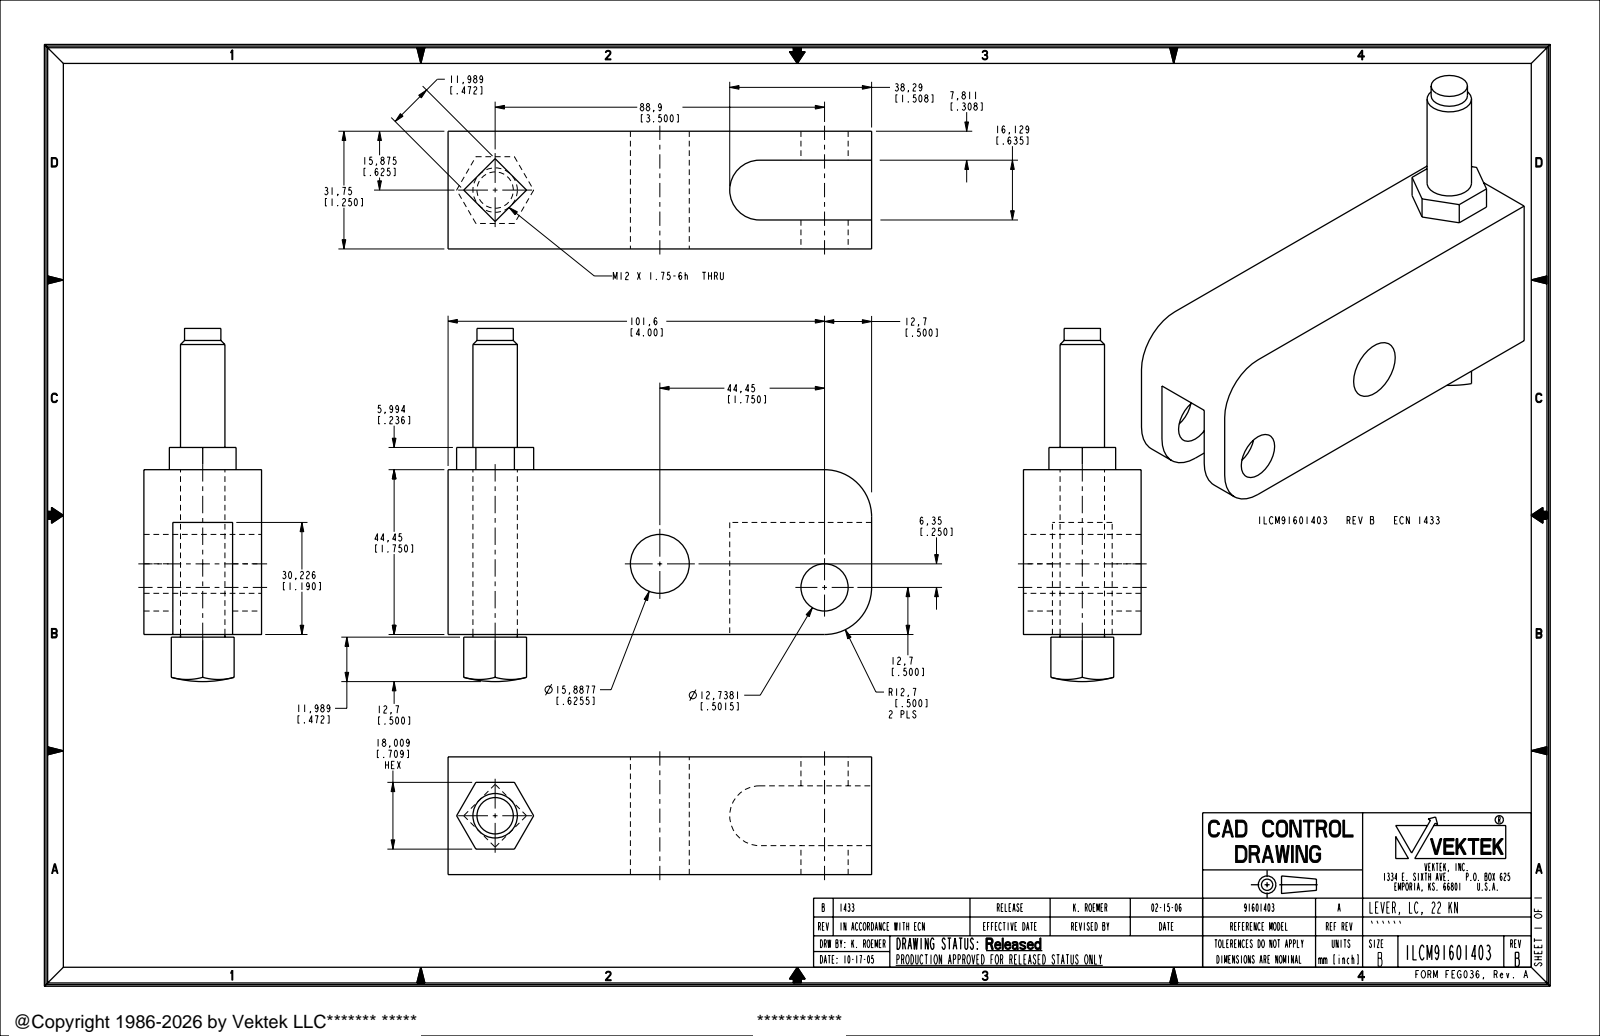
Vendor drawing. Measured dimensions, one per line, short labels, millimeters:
name: ILCM91601403
written by: PRO/ENGINEER BY PARAMETRIC TECHNOLOGY CORPORATION, 2004290 (AUTOMOTIVE_DESIGN_CC2)
unit: mm
bodies: 1 solid, 47 faces (25 planar, 18 cylindrical, 4 other)
size: 114.3 × 95.25 × 31.75
volume: 140 476 mm³; area: 27 023 mm²
holes: 1× ⌀12.74, 1× ⌀15.89
bosses: 1× ⌀11.99, 1× ⌀9.8
rounds: 2× R12.7, 1× R8.06
face distances: 31.76, 44.45, 7.82, 23.94, 16.12, 30.23, 14.22, 114.3, 11.99, 50.44
hole spacings: 44.9
